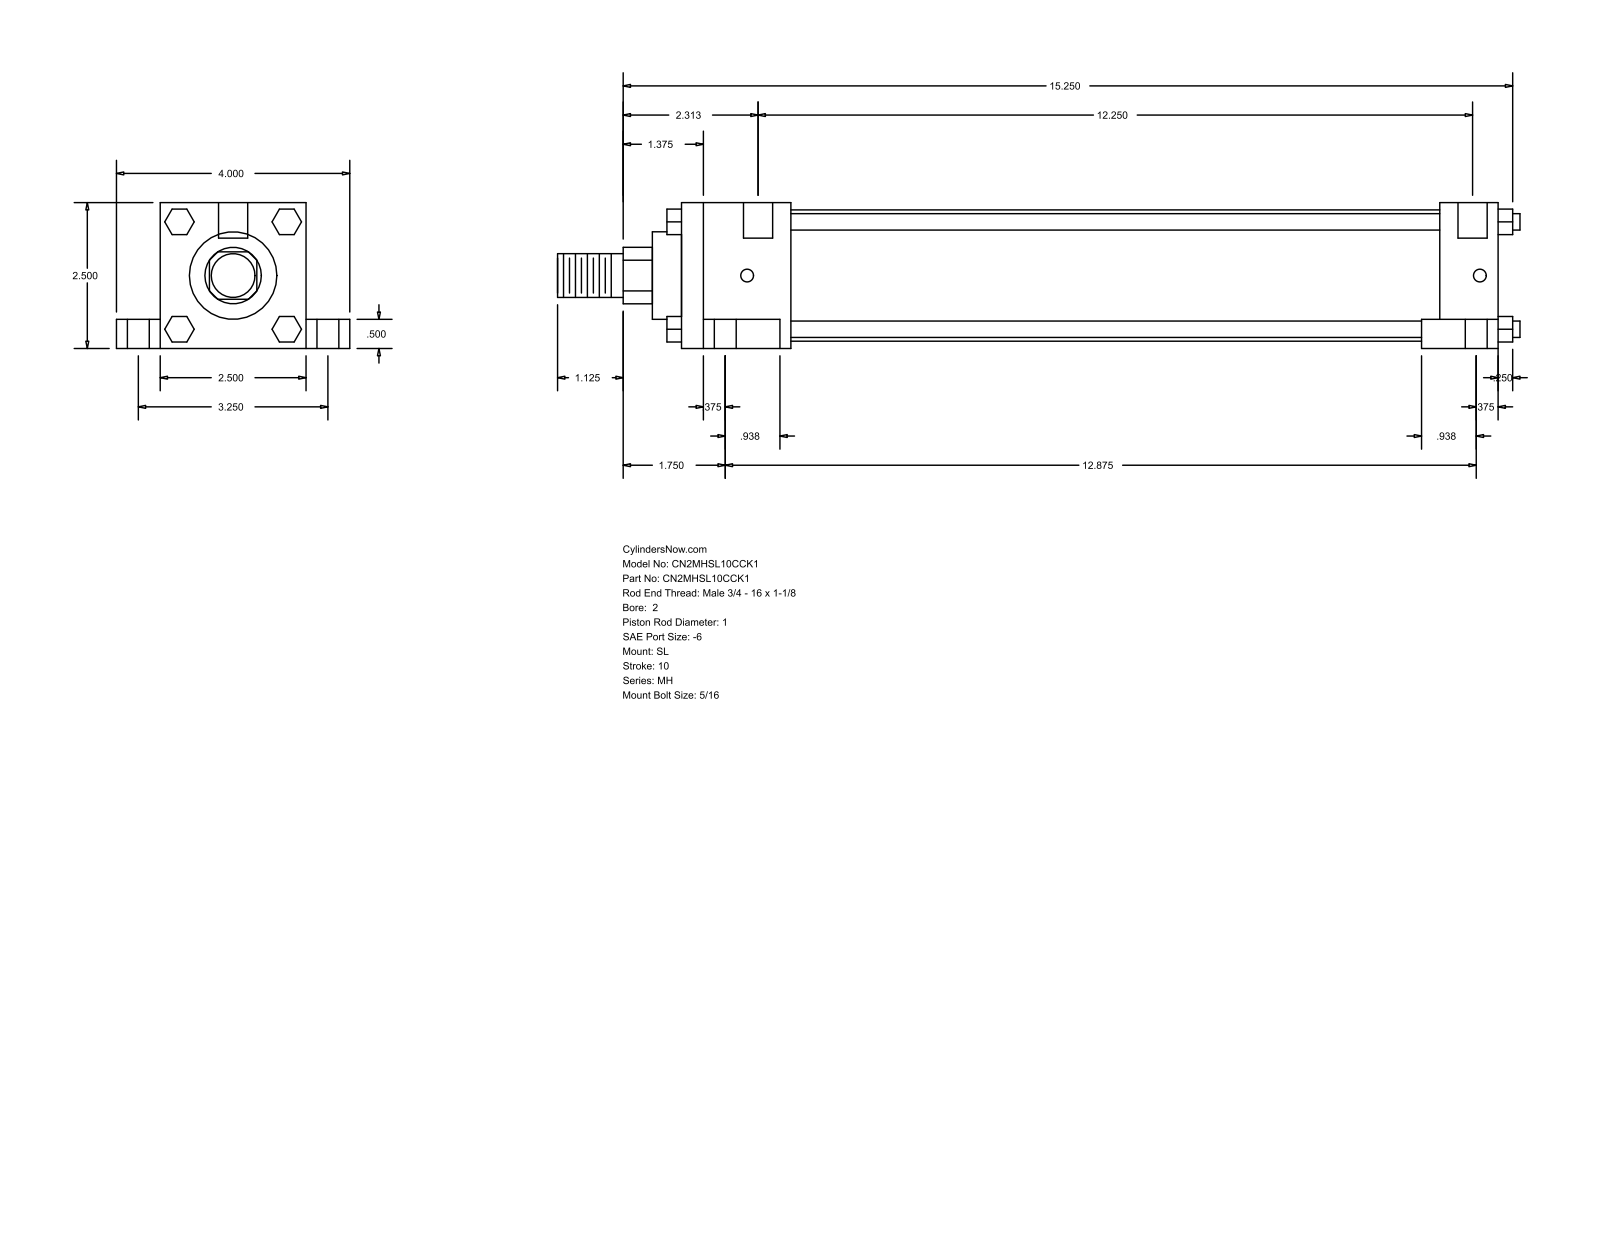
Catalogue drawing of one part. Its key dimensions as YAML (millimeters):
part_name: "MH_SL__0200_1"
step_written_by: "GSSL Pune (CONFIG_CONTROL_DESIGN)"
units: millimeters
bodies: {solids: 0, faces: 148, planar: 112, cylindrical: 36, other: 0}
overall_size: [419.1, 101.6, 63.5]
round_holes:
  - {diameter: 5.56, count: 4}
  - {diameter: 9.53, count: 4}
  - {diameter: 15.88, count: 4}
  - {diameter: 12.7, count: 2}
round_bosses_or_shafts:
  - {diameter: 7.14, count: 4}
  - {diameter: 57.15, count: 1}
  - {diameter: 38.1, count: 1}
  - {diameter: 25.4, count: 1}
  - {diameter: 19.05, count: 1}
partial_cylinders:
  - {radius: 12.29, count: 1}
face_to_face_distances: [63.5, 355.6, 12.7, 19.05, 50.8, 82.55, 25.4, 330.2, 47.63, 282.57]
hole_center_spacings: [41.3, 42.36, 43.67, 82.54, 315.45, 319.08, 320.17, 327.03]
